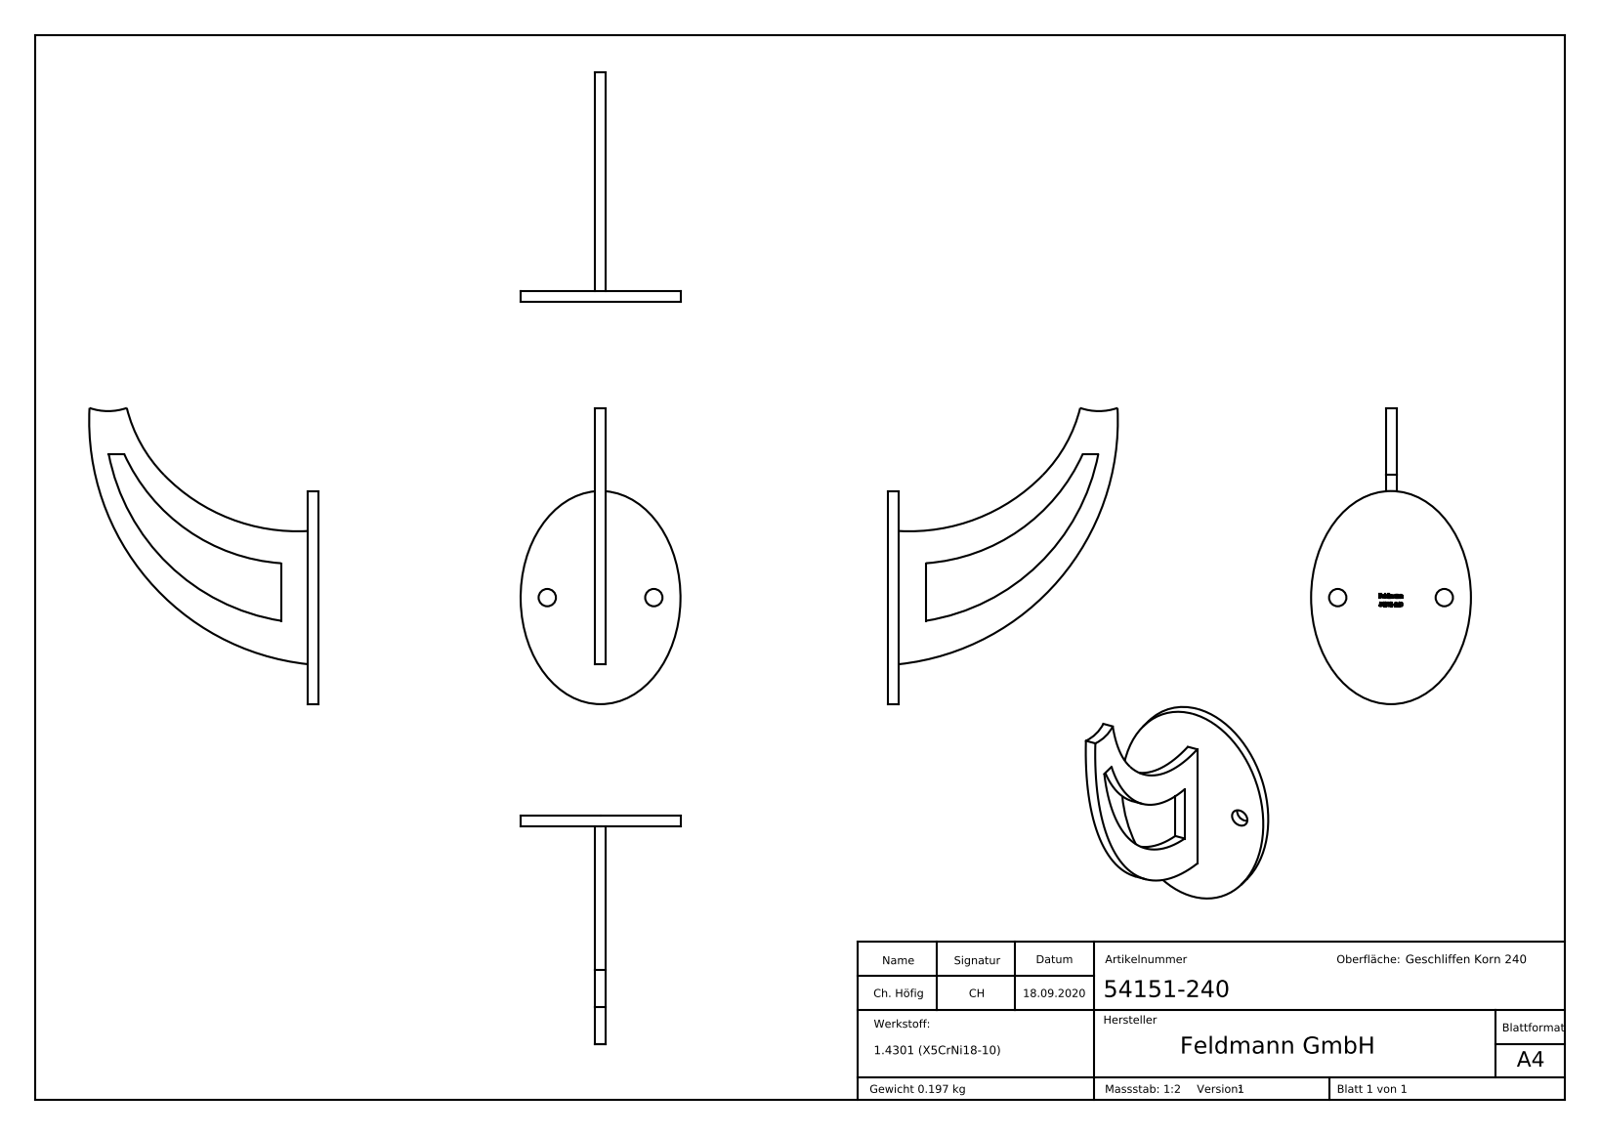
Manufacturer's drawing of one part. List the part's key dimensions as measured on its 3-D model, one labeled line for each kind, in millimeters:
Part name (STEP PRODUCT): 54151-240
STEP written by: SolidWorks 2018 (CONFIG_CONTROL_DESIGN)
Units: millimetres
Bodies: 1 solid, 234 faces (143 planar, 10 cylindrical, 81 other)
Overall size (bounding box): 111.19 × 86.12 × 60
Volume: 24 917 mm³ · Surface area: 15 082 mm²
Round holes (diameter × count): ⌀6.5 ×2
Partial cylindrical surfaces — rounded edges, fillets, slot ends (radius × count): R70 ×2, R21.2 ×1, R55 ×1, R78.5 ×1, R92 ×1
Main face-to-face distances: 4, 14.1, 10.1, 3.9, 14, 1.14, 3.2, 0.88, 2.87, 0.39
Hole centre spacings: 40
